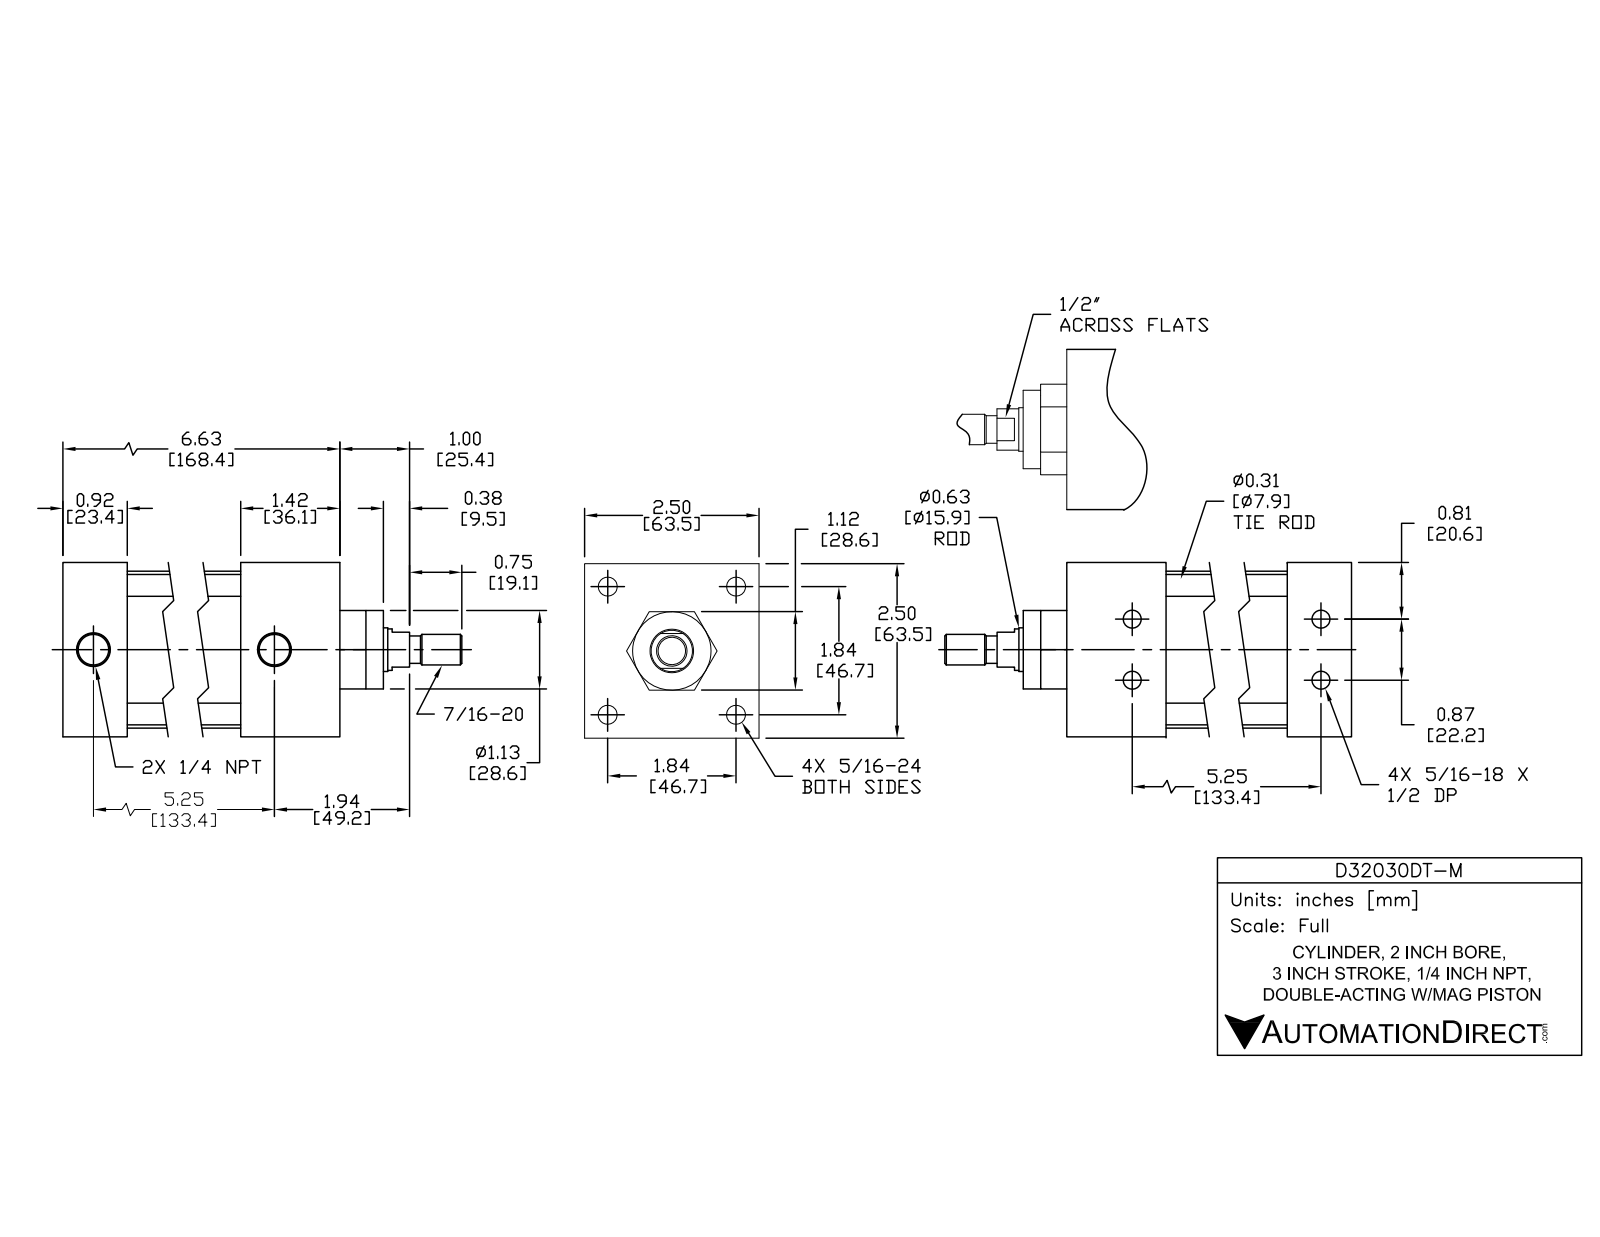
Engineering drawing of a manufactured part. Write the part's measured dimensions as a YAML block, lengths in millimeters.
part_name: "D32030DT-M; D32030DT-M BODY; D32030DT-M PISTON"
step_written_by: "SolidWorks 2015 (AUTOMOTIVE_DESIGN)"
units: millimeters
bodies: {solids: 12, faces: 298, planar: 94, cylindrical: 114, other: 90}
overall_size: [212.6, 63.5, 63.5]
volume: 393300
surface_area: 116200
round_holes:
  - {diameter: 6.4, count: 4}
  - {diameter: 6.8, count: 4}
  - {diameter: 9.1, count: 4}
  - {diameter: 12.7, count: 4}
  - {diameter: 7.5, count: 2}
  - {diameter: 12.1, count: 2}
  - {diameter: 15.9, count: 1}
  - {diameter: 16, count: 1}
  - {diameter: 50.8, count: 1}
round_bosses_or_shafts:
  - {diameter: 12.3, count: 4}
  - {diameter: 8, count: 4}
  - {diameter: 7.2, count: 4}
  - {diameter: 57.2, count: 1}
  - {diameter: 50.7, count: 1}
  - {diameter: 28.4, count: 1}
  - {diameter: 15.8, count: 1}
  - {diameter: 15, count: 1}
partial_cylinders:
  - {radius: 6.4, count: 4}
face_to_face_distances: [63.5, 2, 106.7, 168.2, 36.1, 132.1, 108.7, 144.8, 23.4, 25.4]
hole_center_spacings: [11.1, 133.7, 133.2, 22.2, 33.2, 33.2, 46.9, 46.9]
